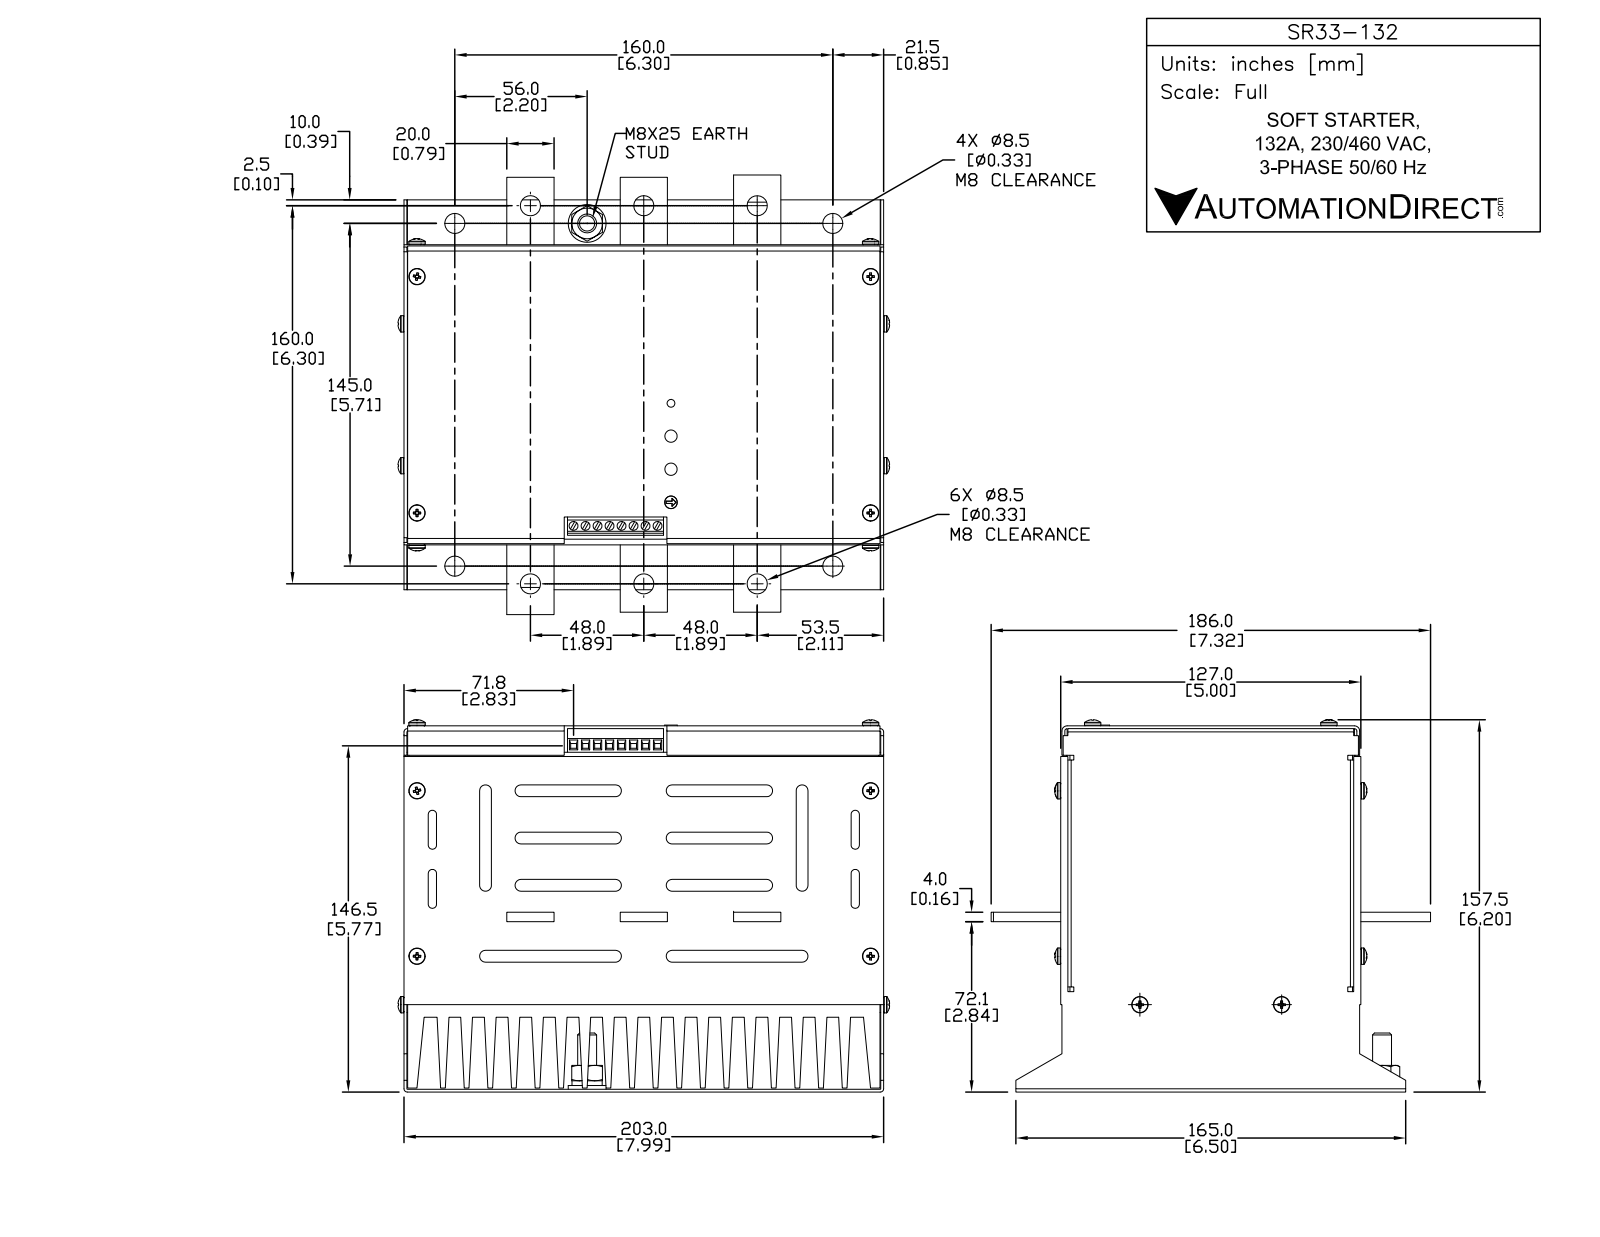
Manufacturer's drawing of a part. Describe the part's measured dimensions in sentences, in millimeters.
The part is named "SR33-132". Its 3-D file was written by "SolidWorks 2013 (AUTOMOTIVE_DESIGN)". It is 1 solid with 881 faces: 580 planar, 155 cylindrical and 146 other. Overall it measures 203 by 186 by 158 millimeters. Its volume is 3 204 000 cubic millimeters and its surface area 529 358 square millimeters. Round holes: 8 of diameter 3.82, 4 of diameter 8.5. Round bosses or shafts: 8 of diameter 6.9, 7 of diameter 16, 6 of diameter 8.5, 1 of diameter 8. Partial cylindrical surfaces (rounded edges, fillets, slot ends): 20 of radius 2.5, 8 of radius 1.75, 4 of radius 1, 2 of radius 2. The main face-to-face distances are 9.99, 19.98, 29.97, 39.96, 49.95, 59.94, 69.93, 79.92, 89.91, 99.9. The hole center spacings are 4.92, 9.84, 14.76, 19.68, 24.6, 29.52, 145, 160.
